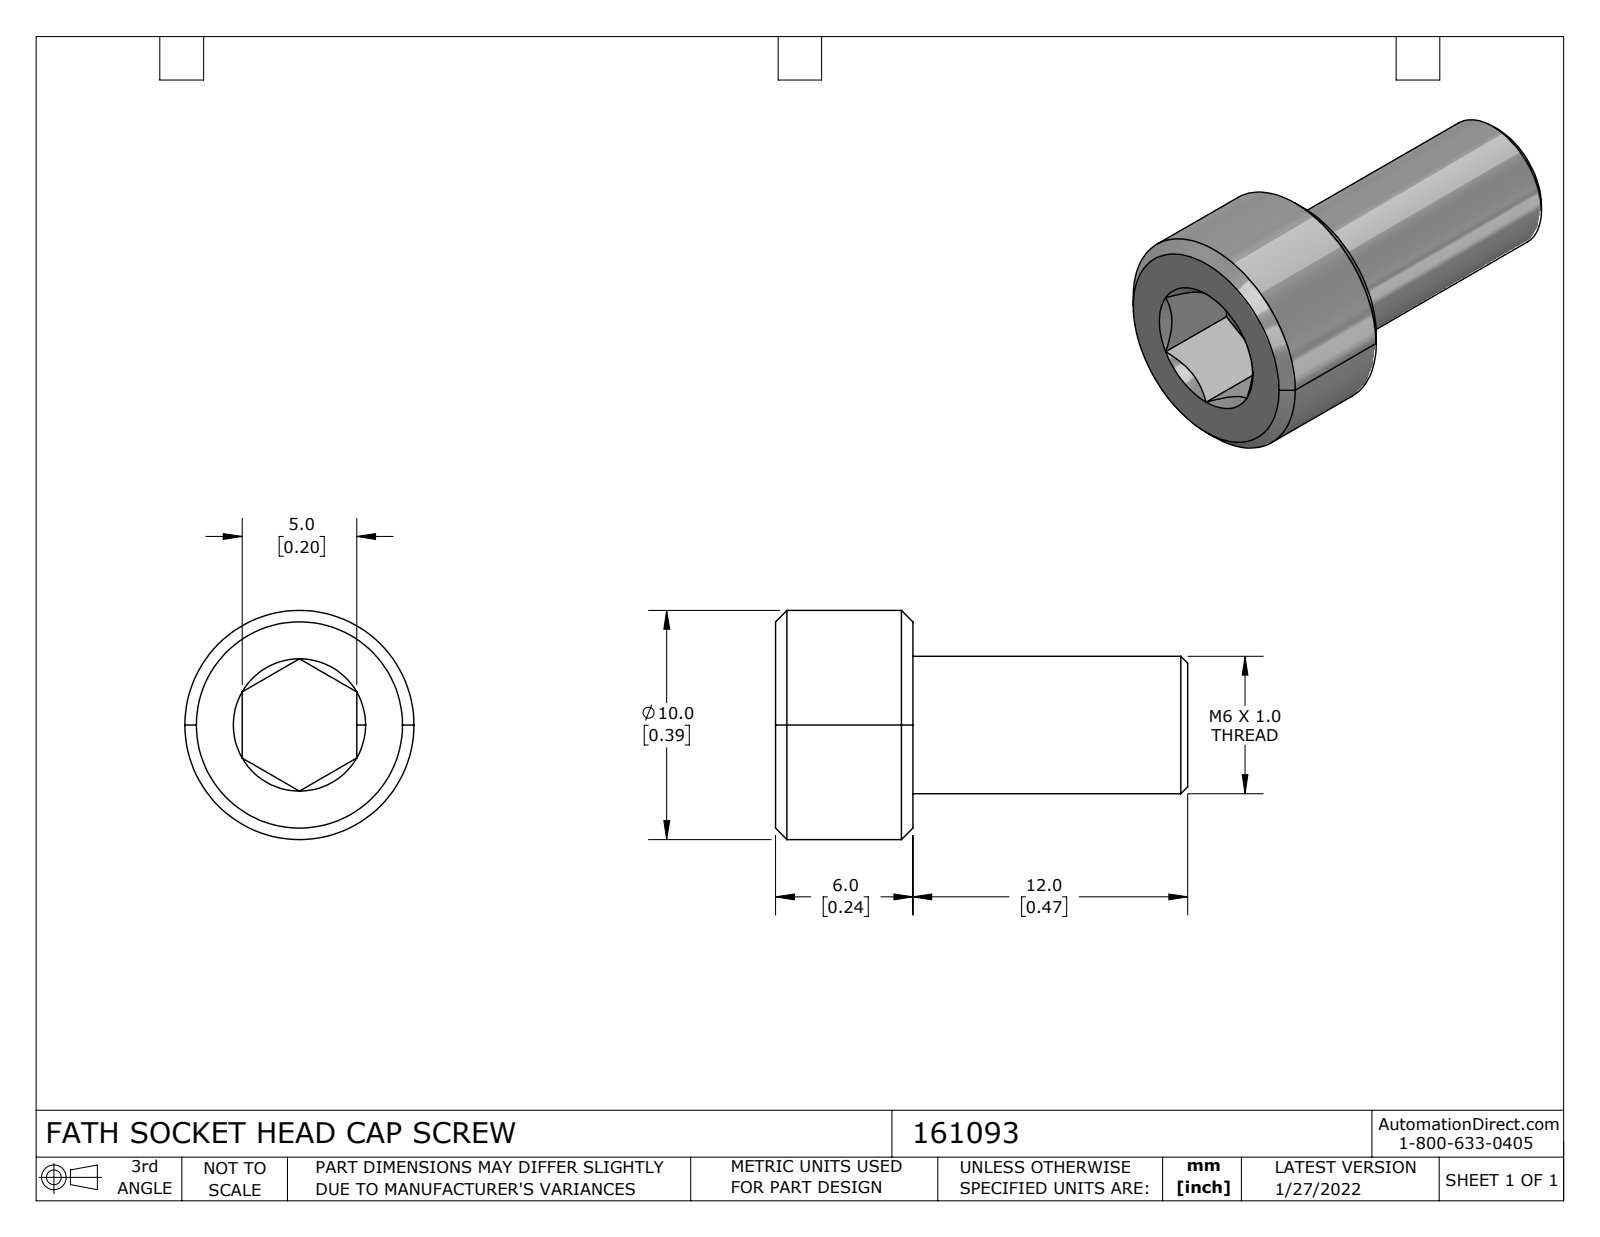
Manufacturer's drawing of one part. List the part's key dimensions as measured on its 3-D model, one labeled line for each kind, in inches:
Part name (STEP PRODUCT): 161093
STEP written by: SolidWorks 2021 (CONFIG_CONTROL_DESIGN)
Units: inches
Bodies: 1 solid, 27 faces (10 planar, 4 cylindrical, 13 other)
Overall size (bounding box): 0.709 × 0.394 × 0.394
Volume: 0.044 in³ · Surface area: 0.949 in²
Round bosses / shafts (diameter × count): ⌀0.394 ×1, ⌀0.236 ×1
Main face-to-face distances: 0.236, 0.197, 0.709, 0.472, 0.148, 0.089, 0.561
